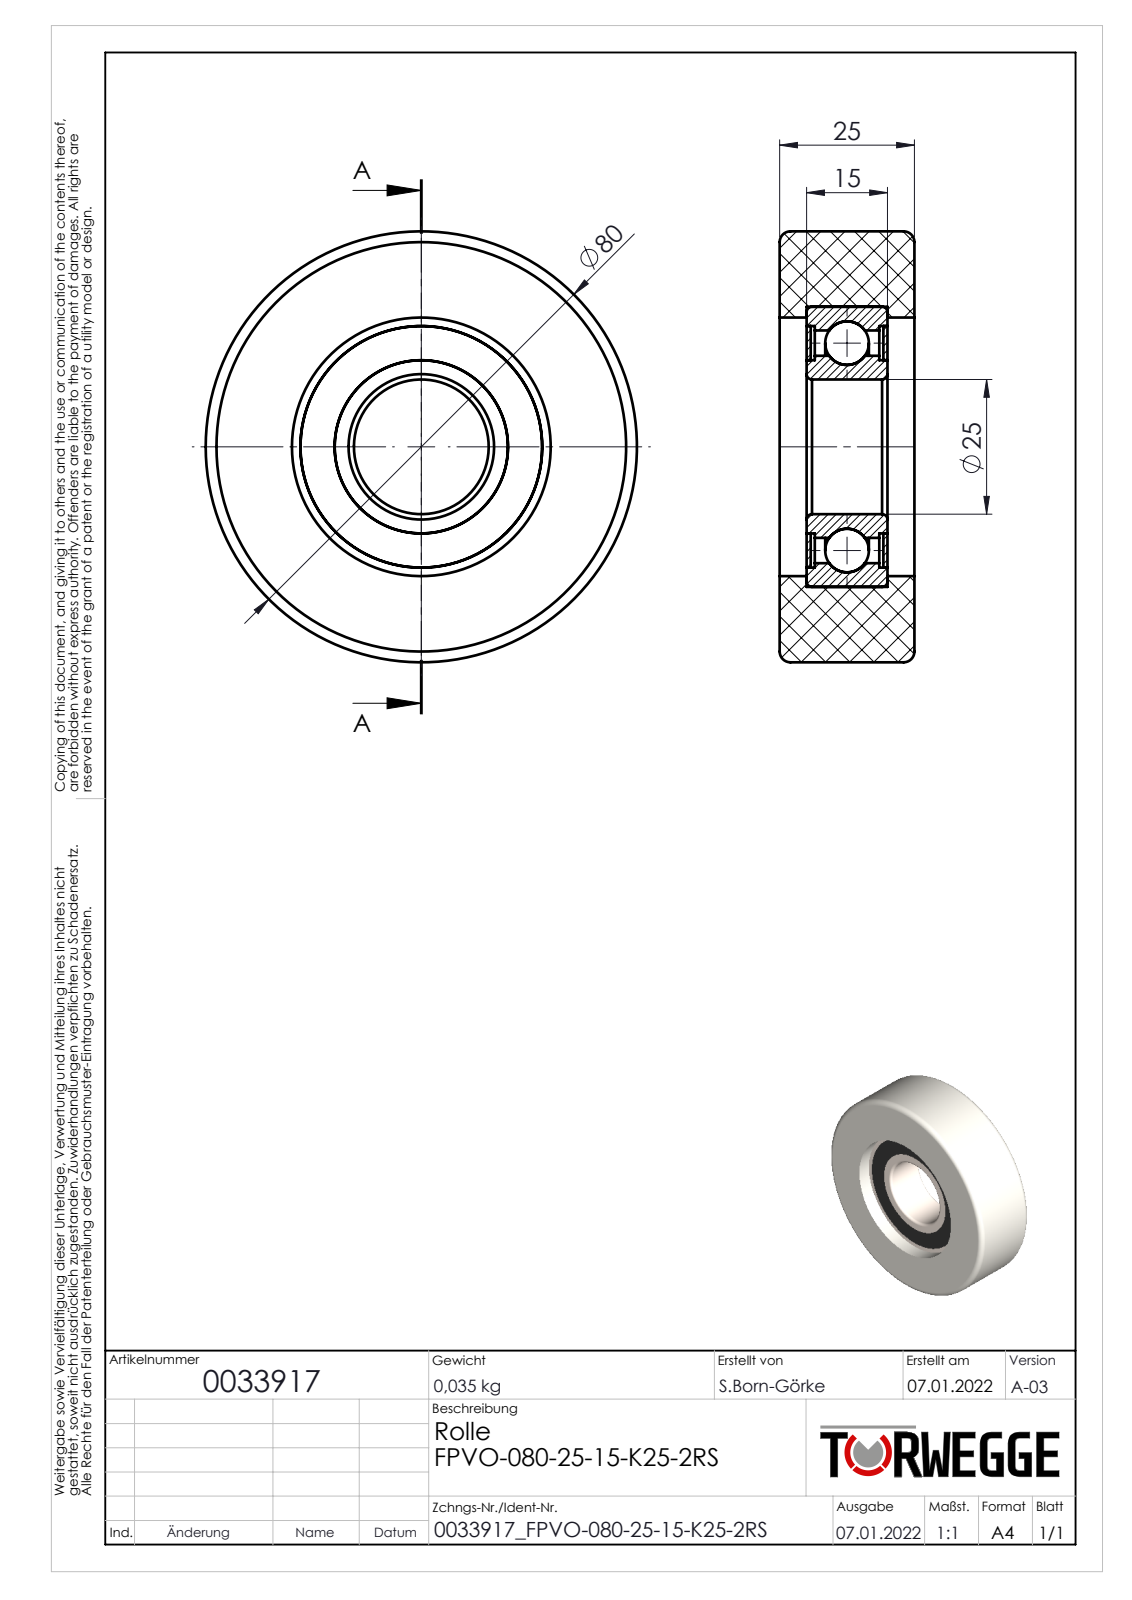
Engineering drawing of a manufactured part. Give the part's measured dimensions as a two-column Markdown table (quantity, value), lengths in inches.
| quantity | value |
| --- | --- |
| part name | 0033917 |
| STEP written by | SolidWorks 2020 (AUTOMOTIVE_DESIGN) |
| units | inches |
| bodies | 0 solids, 34 faces (8 planar, 18 cylindrical, 8 other) |
| overall size | 3.15 × 3.15 × 0.984 |
| round holes (diameter × count) | 0.984 × 1, 1.266 × 1, 1.766 × 1, 1.89 × 1 |
| round bosses / shafts (diameter × count) | 3.15 × 1 |
| main face-to-face distances | 0.197, 0.787, 0.984, 0.591 |
